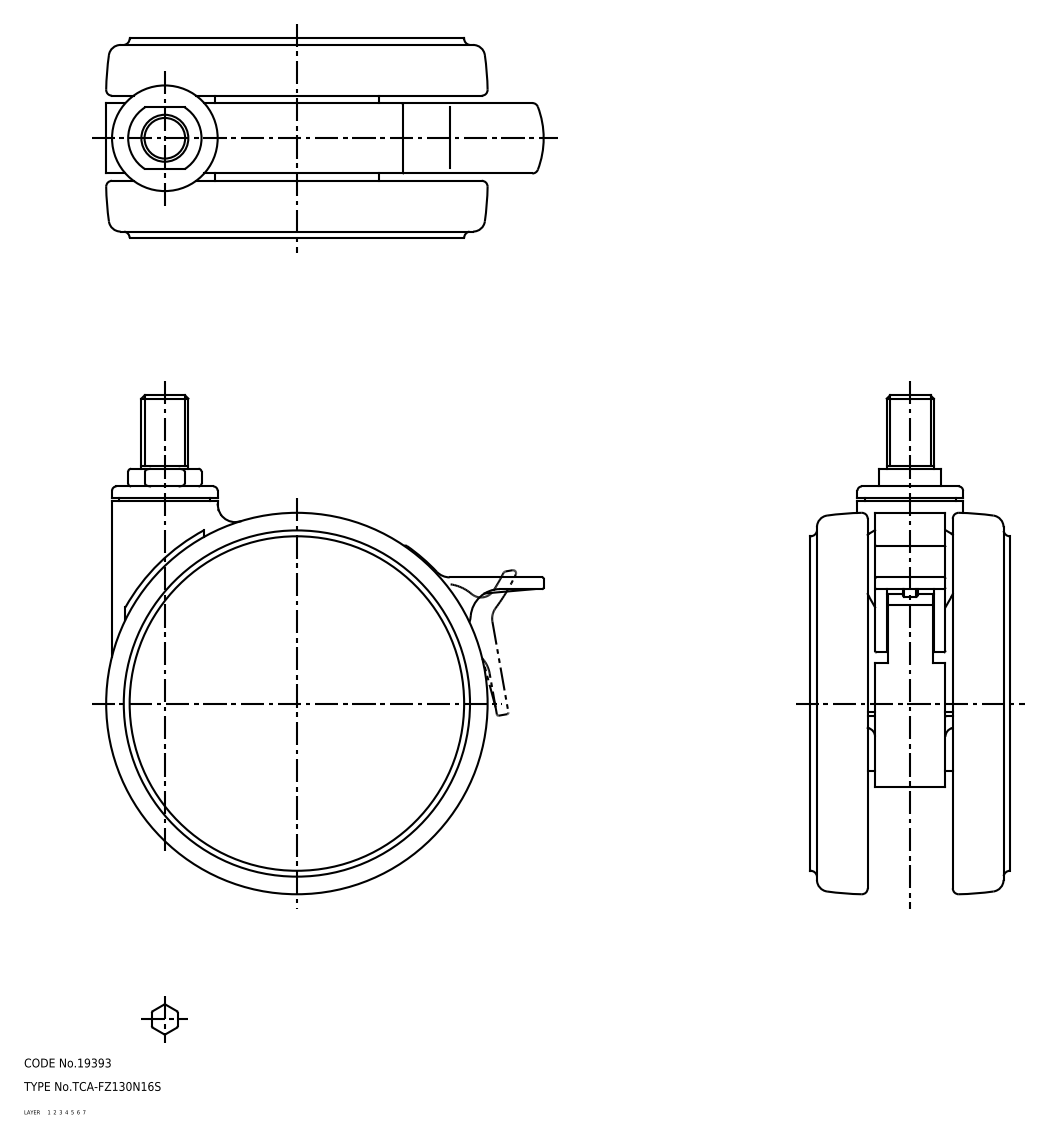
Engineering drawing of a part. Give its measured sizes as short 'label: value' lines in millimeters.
name: caster; TCA-FZ130N16S
written by: SolidWorks 2015 (AUTOMOTIVE_DESIGN)
unit: mm
bodies: 1 solid, 2579 faces (767 planar, 1112 cylindrical, 700 other)
size: 170 × 149.11 × 68.2
volume: 516 255 mm³; area: 193 178 mm²
holes: 2× ⌀3, 2× ⌀3.25, 1× ⌀1.8, 1× ⌀3.2, 1× ⌀9.1, 1× ⌀10, 1× ⌀10.1, 1× ⌀10.5, 1× ⌀11.5, 1× ⌀12, 1× ⌀15, 1× ⌀15.2
bosses: 1× ⌀117.8, 1× ⌀114, 1× ⌀42, 1× ⌀36, 1× ⌀31, 1× ⌀27.9, 1× ⌀27.6, 1× ⌀20
rounds: 126× R0.5, 110× R1.5, 74× R1, 44× R0.3, 19× R2, 16× R0.2, 9× R3, 5× R4
face distances: 2, 66.2, 1.8, 3.8, 62.4, 64.4, 11.3, 7.5, 56.9, 9.3
hole spacings: 31.24, 39.66, 57.03
